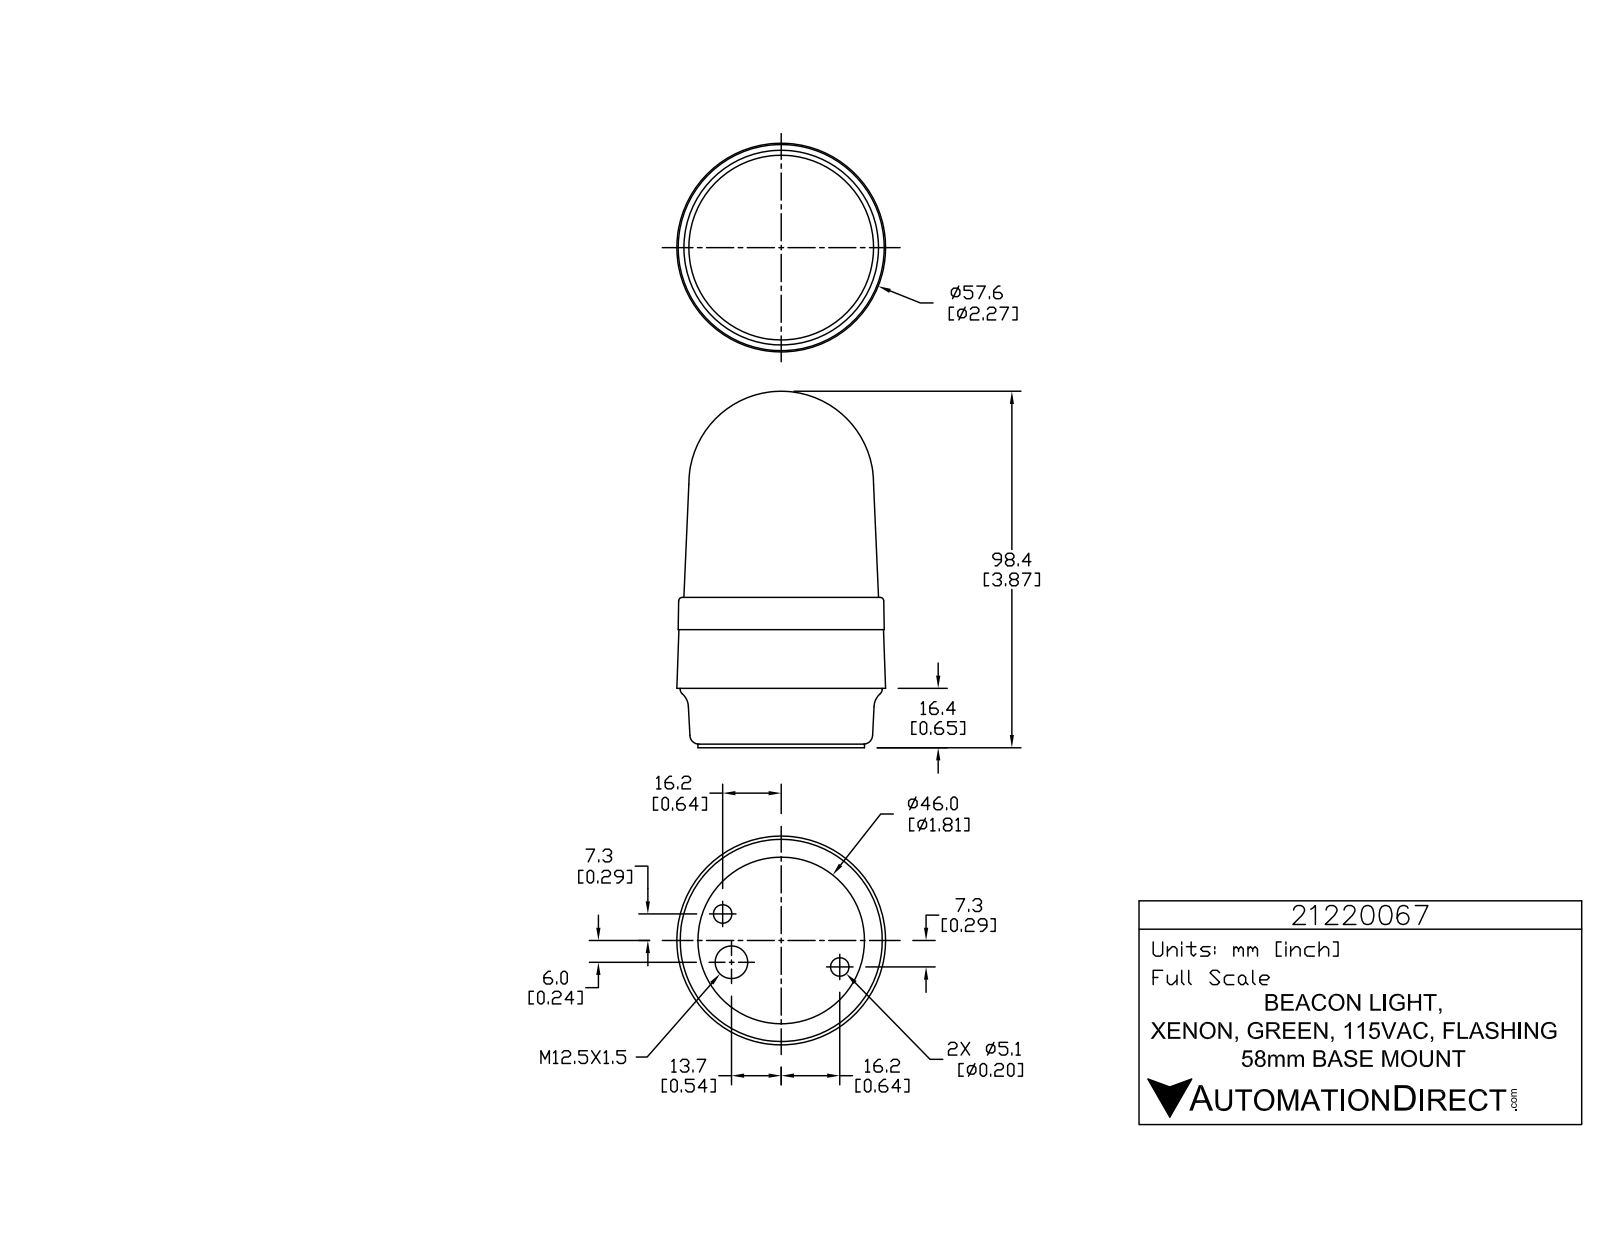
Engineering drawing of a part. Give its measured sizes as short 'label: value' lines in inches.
name: 21220067
written by: SolidWorks 2015 (AUTOMOTIVE_DESIGN)
unit: in
bodies: 1 solid, 764 faces (527 planar, 145 cylindrical, 92 other)
size: 3.874 × 2.269 × 2.269
volume: 12.2 in³; area: 29.33 in²
holes: 3× ⌀0.039, 2× ⌀0.201, 1× ⌀0.354
bosses: 3× ⌀0.226, 3× ⌀0.056, 1× ⌀2.197, 1× ⌀1.811
rounds: 6× R0.008, 6× R0.008, 6× R0.008, 6× R0.131, 3× R0.004, 3× R0.005, 3× R0.007, 3× R0.008
face distances: 0.646, 0.039, 0.606, 1.634, 1.594, 0.988, 1.283, 1.244, 0.638, 0.35
hole spacings: 0.534, 1.179, 1.398
